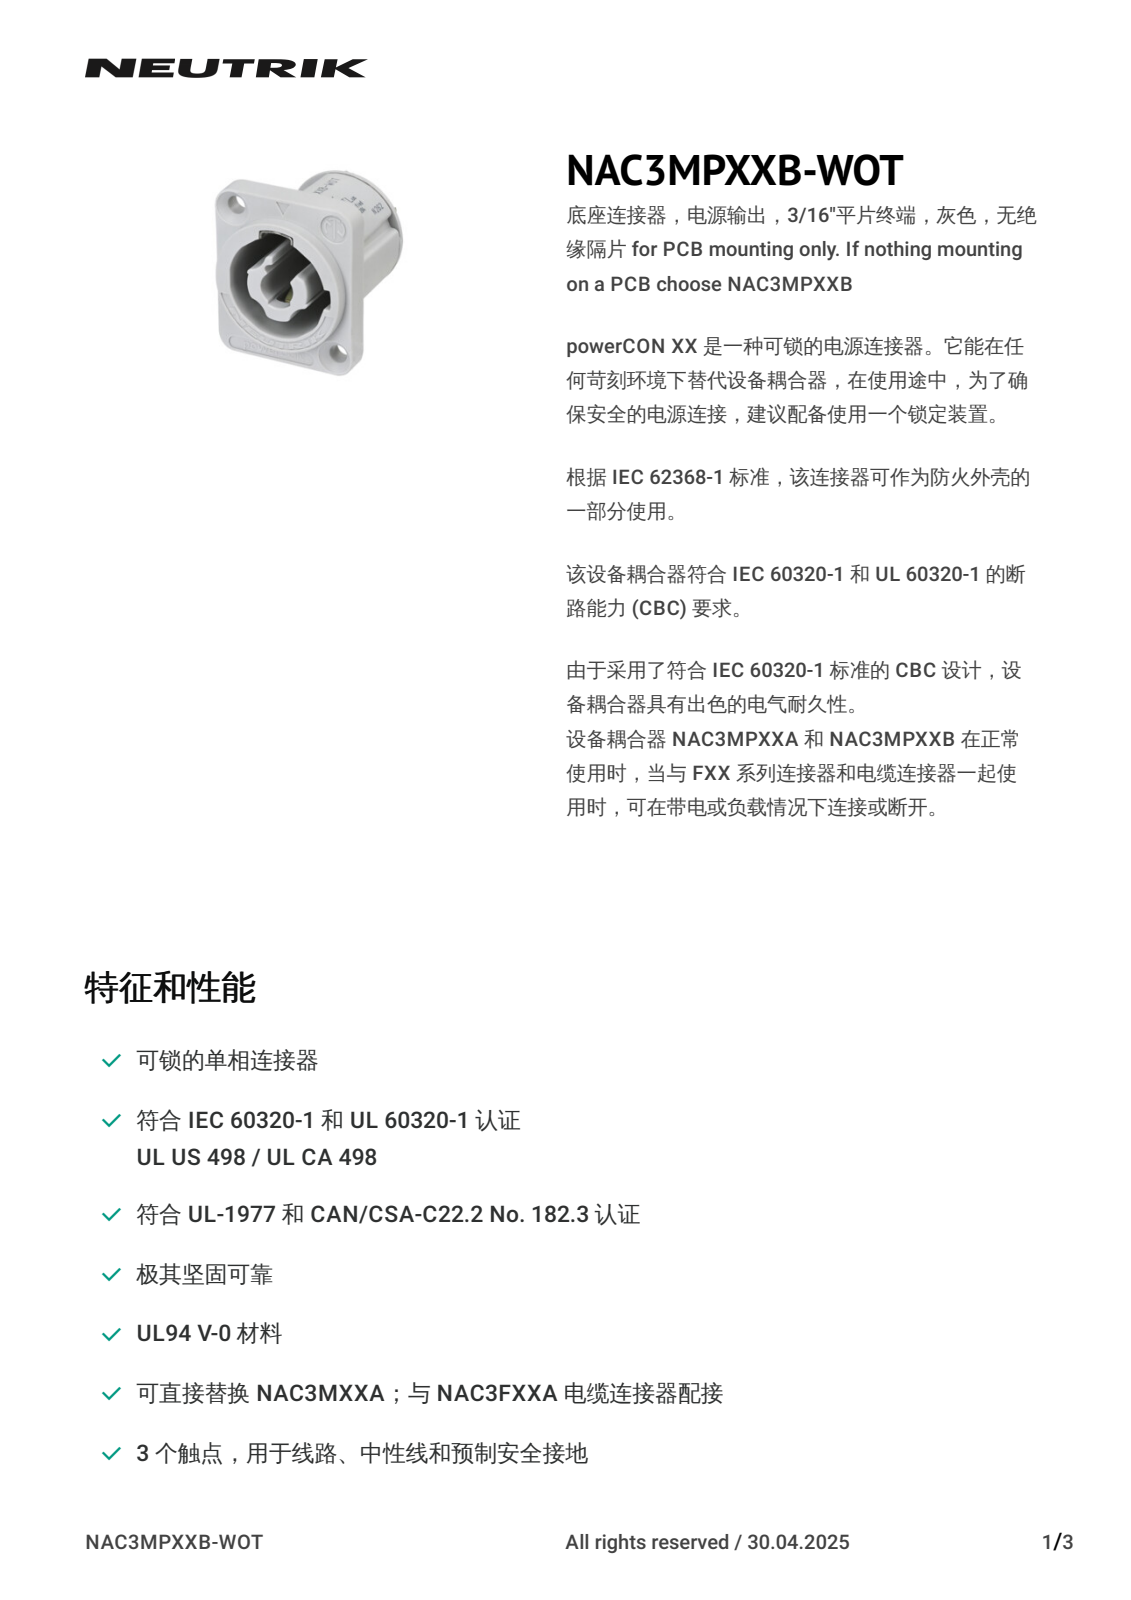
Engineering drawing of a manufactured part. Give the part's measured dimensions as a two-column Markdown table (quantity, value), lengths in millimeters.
| quantity | value |
| --- | --- |
| part name | NAC3MPXXA-WOT |
| STEP written by | CREO PARAMETRIC BY PTC INC, 2019080 (CONFIG_CONTROL_DESIGN) |
| units | millimeters |
| bodies | 1 solid, 1213 faces (364 planar, 184 cylindrical, 665 other) |
| overall size | 34.3 × 30.9 × 25.9 |
| volume | 10 510 mm³ |
| surface area | 5 706 mm² |
| round holes (diameter × count) | 1.4 × 2, 6 × 2, 4.2 × 1, 5 × 1 |
| round bosses / shafts (diameter × count) | 22.5 × 1, 19.6 × 1, 3.65 × 1 |
| partial cylindrical surfaces (radius × count) | 0.2 × 53, 0.5 × 21, 0.3 × 20, 0.25 × 11, 0.21 × 9, 0.14 × 7, 0.28 × 3, 0.15 × 2 |
| main face-to-face distances | 4.55, 2.5, 23.6, 23.55, 4.5, 19.05, 2.55, 26.1, 7.05, 20.45 |
| hole center spacings | 20.83, 10.96, 19, 24, 30.61 |
